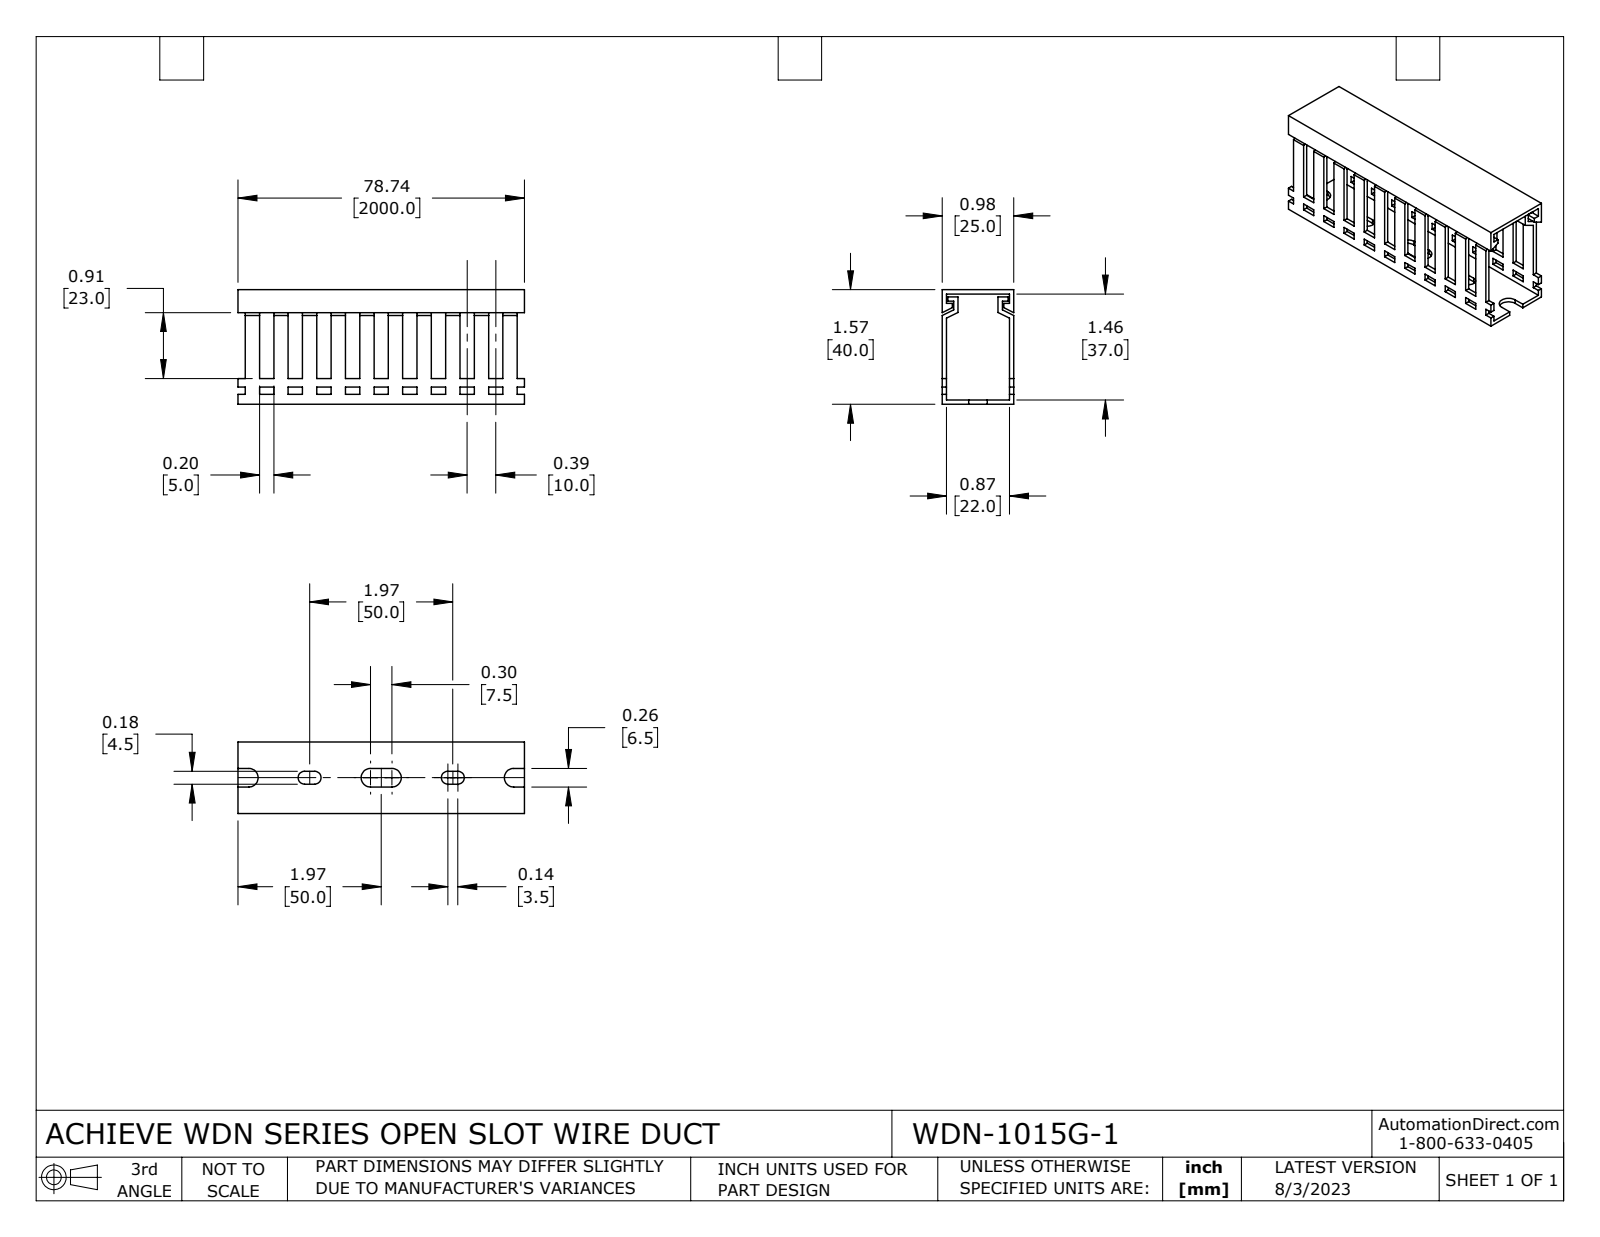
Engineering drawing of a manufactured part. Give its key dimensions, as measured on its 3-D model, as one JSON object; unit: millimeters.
{"part_name": "WDN-1015G-1", "step_written_by": "SolidWorks 2021 (CONFIG_CONTROL_DESIGN)", "units": "millimeters", "bodies": {"solids": 2, "faces": 336, "planar": 324, "cylindrical": 12, "other": 0}, "overall_size": [100, 40, 25], "volume_mm3": 16620, "surface_area_mm2": 25190, "partial_cylinders_radius": [[2.3, 4], [3.3, 4]], "face_to_face_distances": [1.5, 38.5, 23.5, 25, 40, 22, 37, 5, 20, 10]}
